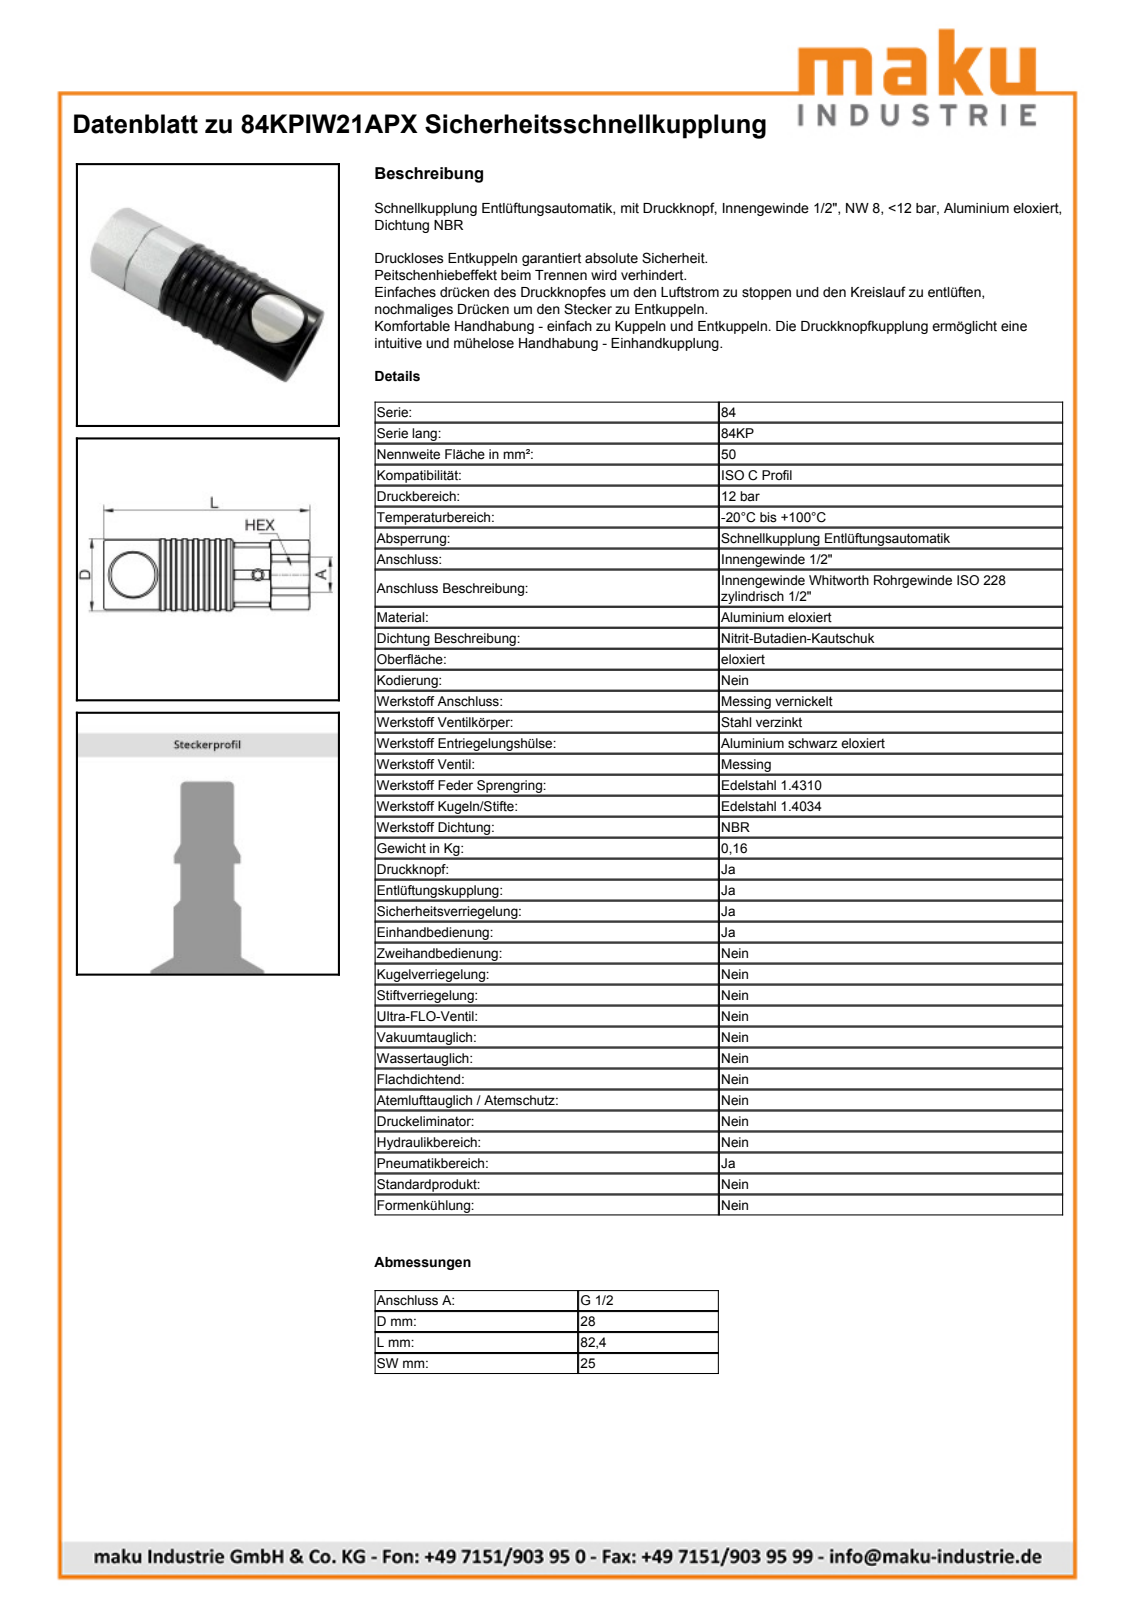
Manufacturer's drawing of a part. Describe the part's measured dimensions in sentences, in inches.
The part is named "84KPIW21APX". Its 3-D file was written by "Autodesk Inventor 2019 (CONFIG_CONTROL_DESIGN)". It is 33 solids with 344 faces: 114 planar, 122 cylindrical and 108 other. Overall it measures 3.244 by 1.102 by 1.102 inches. Its volume is 3.166 cubic inches and its surface area 49.49 square inches. Round holes: 2 of diameter 0.138, 2 of diameter 0.157, 2 of diameter 0.551, 1 of diameter 0.311, 1 of diameter 0.315, 1 of diameter 0.441, 1 of diameter 0.555, 1 of diameter 0.61, 1 of diameter 0.657, 1 of diameter 0.659, 1 of diameter 0.673, 1 of diameter 0.709. Round bosses or shafts: 1 of diameter 1.102, 1 of diameter 1.063, 1 of diameter 0.984, 1 of diameter 0.919, 1 of diameter 0.917, 1 of diameter 0.906, 1 of diameter 0.85, 1 of diameter 0.776. Partial cylindrical surfaces (rounded edges, fillets, slot ends): 1 of radius 0.218, 1 of radius 0.335, 1 of radius 0.366, 1 of radius 0.384, 1 of radius 0.531, 1 of radius 0.571. The main face-to-face distances are 0.984, 2.535, 1.39, 1.146, 0.957, 0.252, 0.037, 1.427, 2.572, 0.894. The hole center spacings are 0.047, 0.051, 0.866, 1.028, 1.894.
